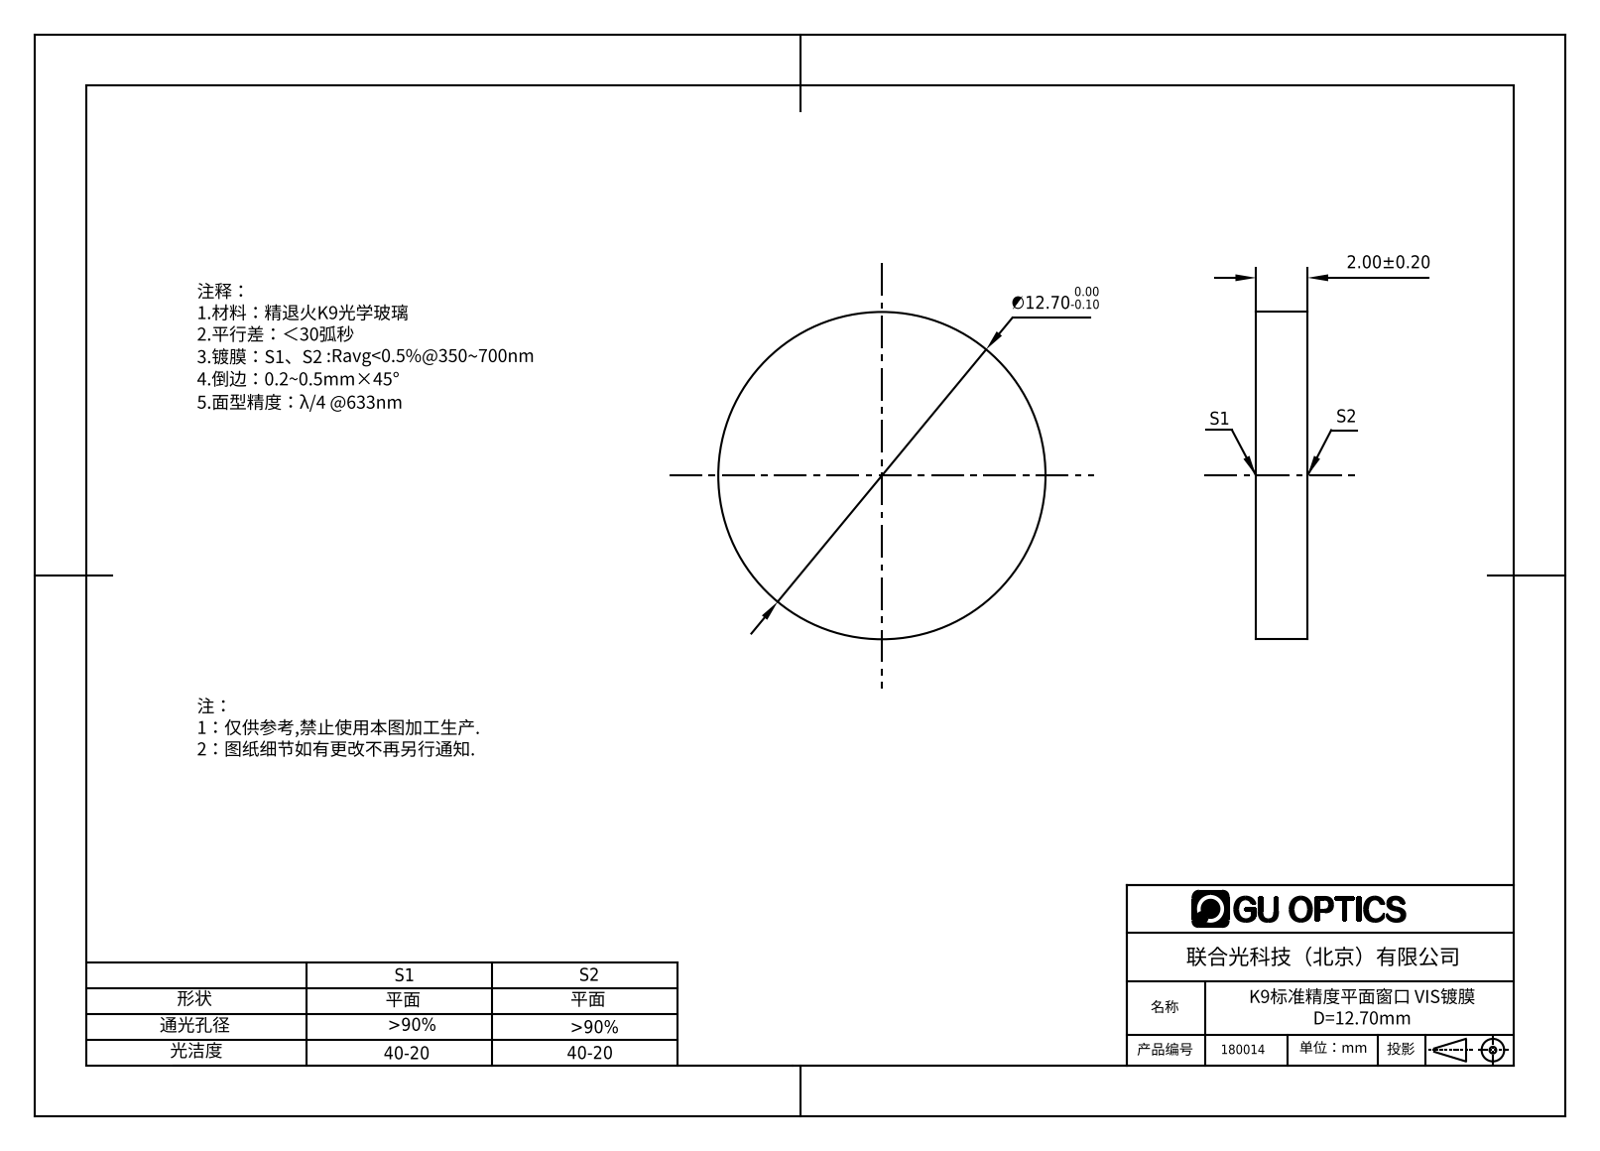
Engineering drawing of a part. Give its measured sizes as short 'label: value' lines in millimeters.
name: 180003
written by: SolidWorks 2016 (AUTOMOTIVE_DESIGN)
unit: mm
bodies: 1 solid, 4 faces (2 planar, 2 cylindrical, 0 other)
size: 12.7 × 12.7 × 2
volume: 253 mm³; area: 333 mm²
bosses: 1× ⌀12.7
face distances: 2
